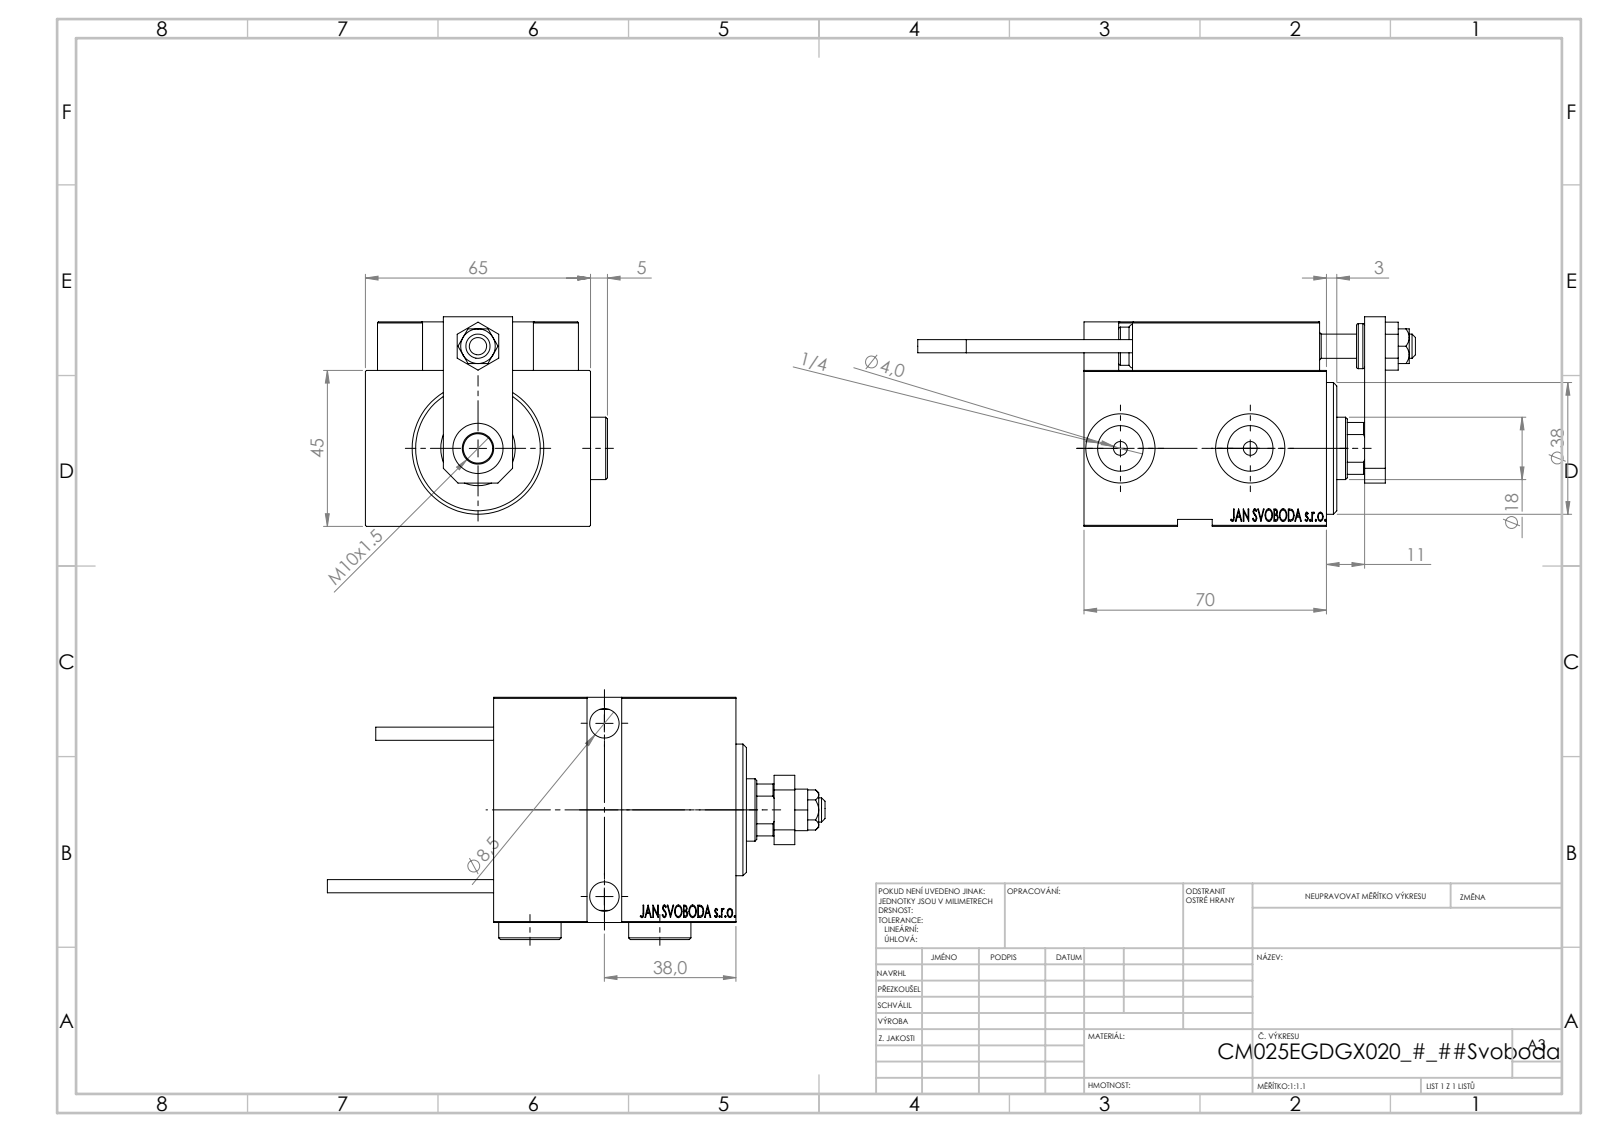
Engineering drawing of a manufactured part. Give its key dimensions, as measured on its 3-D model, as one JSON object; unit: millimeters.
{"part_name": "MAGNET; ALLEN BOLT D5; SWITCH_X_FRONT_BACK; ALLEN BOLT D8 (+7 more)", "step_written_by": "SolidWorks 2019 (CONFIG_CONTROL_DESIGN)", "units": "millimeters", "bodies": {"solids": 26, "faces": 1337, "planar": 602, "cylindrical": 190, "other": 545}, "overall_size": [143.7, 69.9, 60.5], "volume_mm3": 235213, "surface_area_mm2": 66338, "round_holes": [[4, 6], [8, 5], [3.2, 4], [8.5, 3], [5, 2], [13.16, 2], [13.5, 2], [20, 2], [7, 1], [14.5, 1], [18, 1], [21.5, 1]], "round_bosses_or_shafts": [[18, 2], [5, 2], [3.8, 2], [38, 1], [27, 1], [13, 1], [11, 1]], "partial_cylinders_radius": [[0.3, 30], [3, 2], [8.5, 1]], "face_to_face_distances": [45, 65, 59, 14, 6, 19, 8, 13, 70, 3], "hole_center_spacings": [11.37, 20, 22.09, 29.59, 29.69, 30.89, 31.11, 34.17]}
